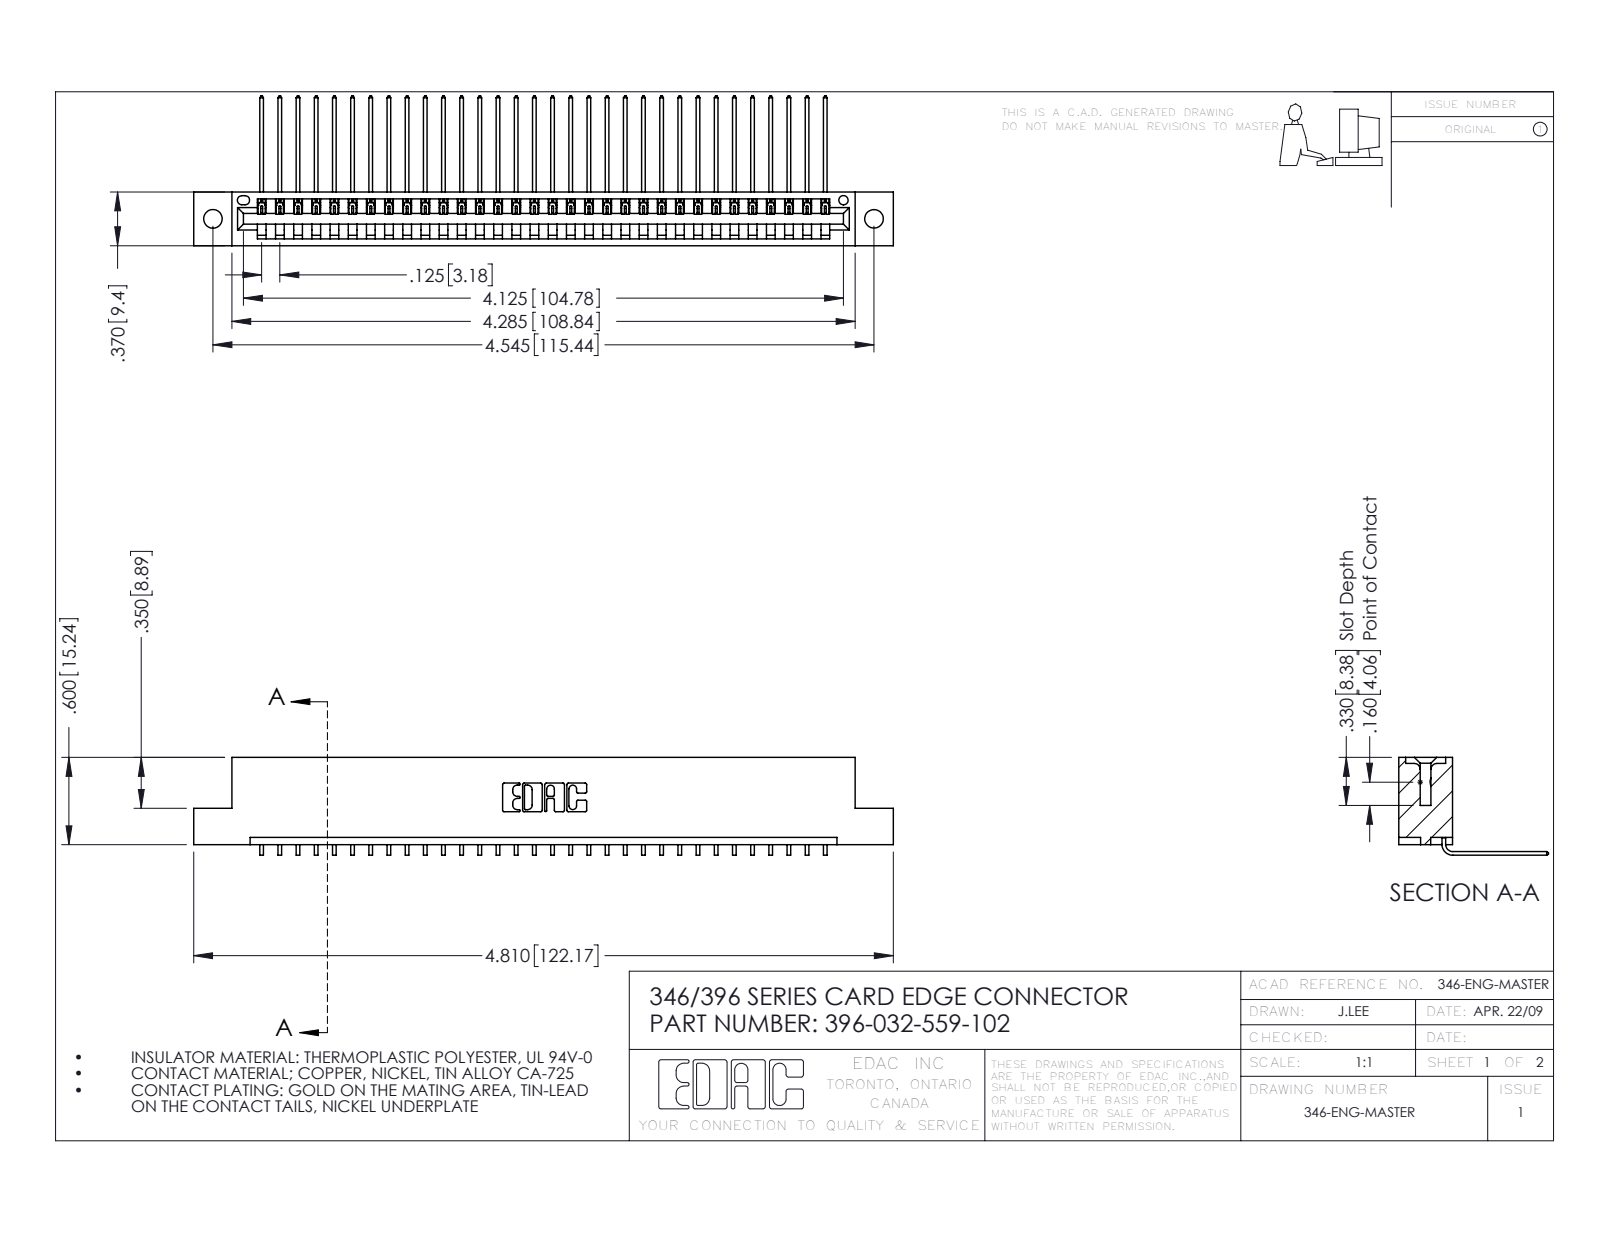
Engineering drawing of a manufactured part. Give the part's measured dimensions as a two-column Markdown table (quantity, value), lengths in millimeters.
| quantity | value |
| --- | --- |
| part name | 346 Part_Flush Mounting Lugs - 0.128 Dia; 345-292-001_558 559 Tail - 1; 396-032-559-102 |
| STEP written by | SolidWorks 2016 (CONFIG_CONTROL_DESIGN) |
| units | millimeters |
| bodies | 33 solids, 2042 faces (1420 planar, 622 cylindrical, 0 other) |
| overall size | 122.2 × 26.2 × 17.1 |
| volume | 11 700 mm³ |
| surface area | 14 880 mm² |
| round holes (diameter × count) | 3.3 × 2, 1.6 × 1 |
| partial cylindrical surfaces (radius × count) | 0.2 × 64, 0.3 × 22, 0.2 × 6, 0.8 × 6, 0.7 × 3, 0.8 × 2, 1 × 2, 0.4 × 1 |
| main face-to-face distances | 1.2, 8.2, 9.4, 6.4, 1.8, 0.6, 7.6, 3.8, 5.6, 2.5 |
| hole center spacings | 6.2, 110.2, 115.4 |
